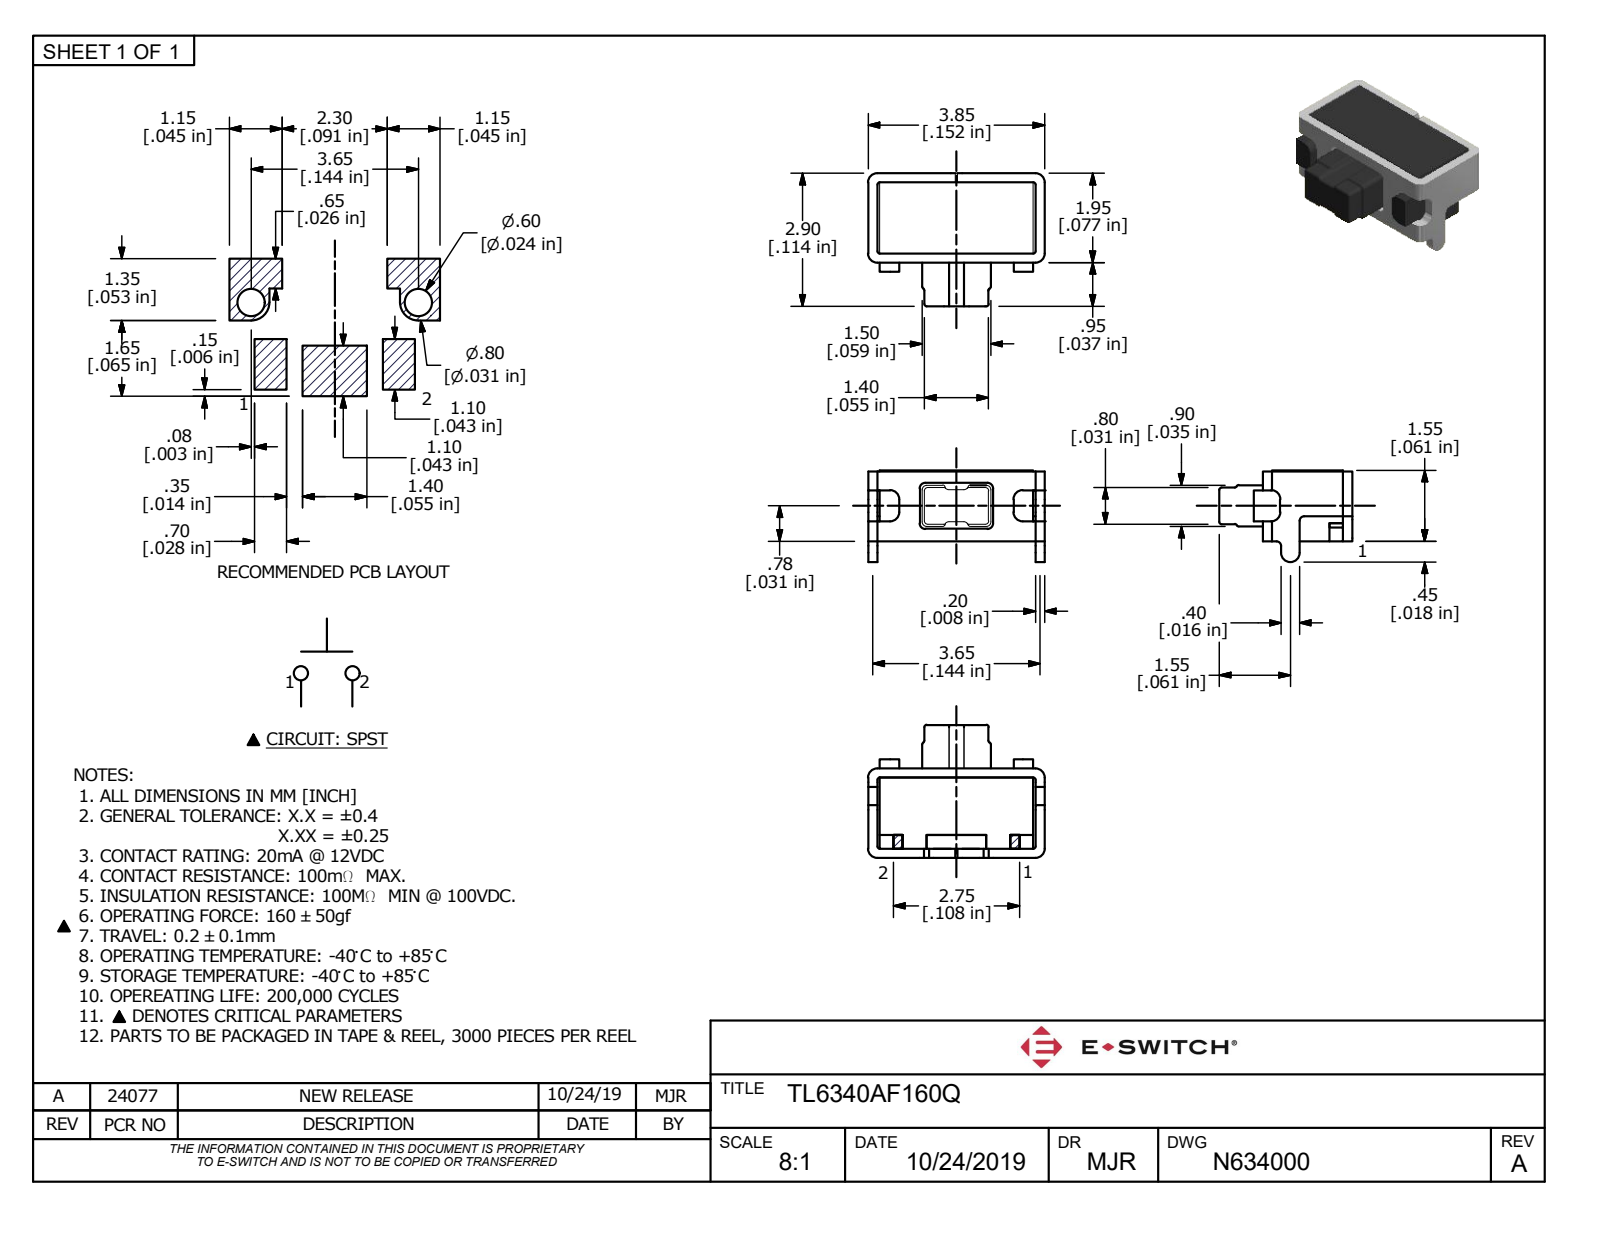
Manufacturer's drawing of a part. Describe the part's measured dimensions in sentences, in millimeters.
The part is named "TL6340AF160Q". Its 3-D file was written by "Autodesk Inventor 2020 (AUTOMOTIVE_DESIGN)". It is 1 solid with 207 faces: 83 planar, 88 cylindrical and 36 other. Overall it measures 3.85 by 2.9 by 2 millimeters. Its volume is 12 cubic millimeters and its surface area 48 square millimeters. Partial cylindrical surfaces (rounded edges, fillets, slot ends): 22 of radius 0.1, 11 of radius 0.2, 4 of radius 0.12, 4 of radius 0.14, 2 of radius 0.3. The main face-to-face distances are 1.56, 3.61, 3.66, 3.41, 1.94, 3.36, 0.98, 1.53, 3.86, 3.46.
